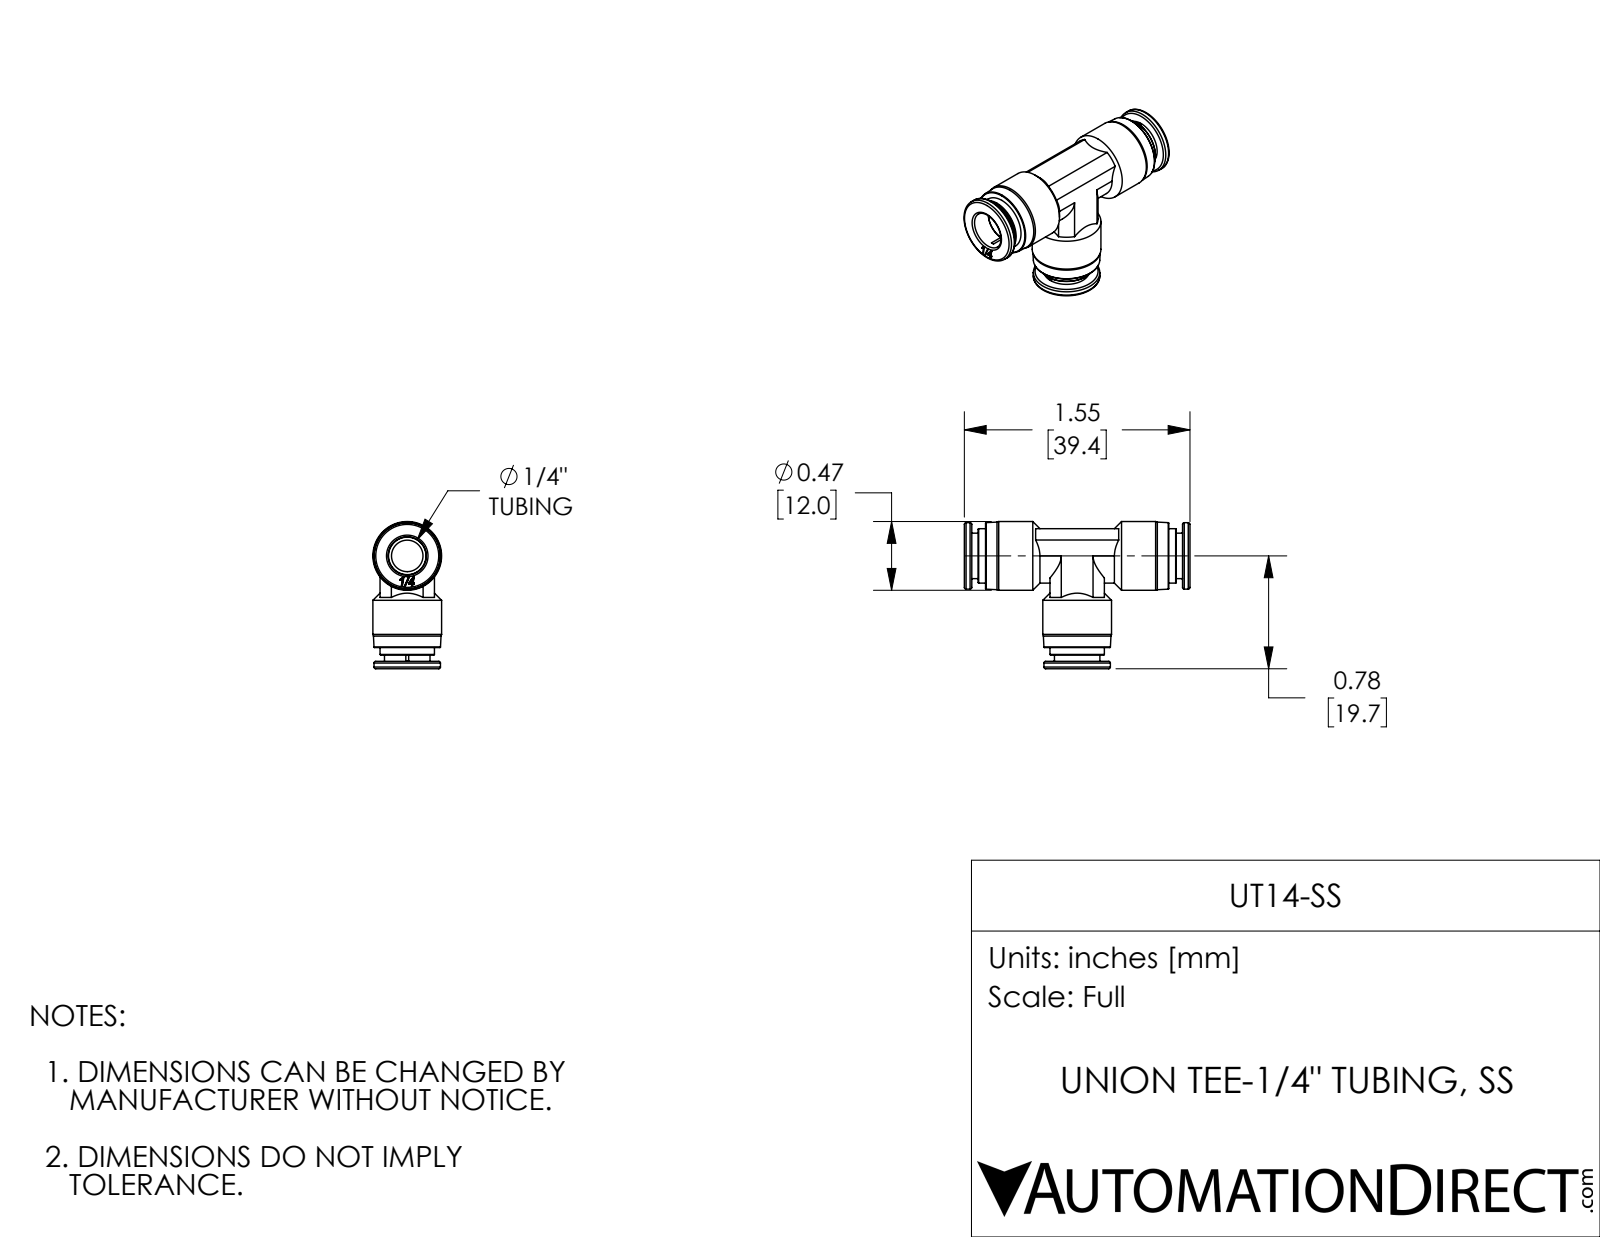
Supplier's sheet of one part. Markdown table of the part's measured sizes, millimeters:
| quantity | value |
| --- | --- |
| part name | UT14-SS |
| STEP written by | SolidWorks 2017 (AUTOMOTIVE_DESIGN) |
| units | millimeters |
| bodies | 1 solid, 243 faces (122 planar, 55 cylindrical, 66 other) |
| overall size | 39.4 × 25.7 × 12 |
| volume | 3 332 mm³ |
| surface area | 3 722 mm² |
| round holes (diameter × count) | 5.5 × 2, 6.55 × 2, 6.65 × 2, 8.1 × 2 |
| round bosses / shafts (diameter × count) | 12 × 2, 11.6 × 2, 9.5 × 2, 7.95 × 2 |
| partial cylindrical surfaces (radius × count) | 5.5 × 2 |
| main face-to-face distances | 1.3, 2.4, 3.7, 38.1, 9.5, 35.7, 24.45, 23.15, 34.4, 20.75 |
